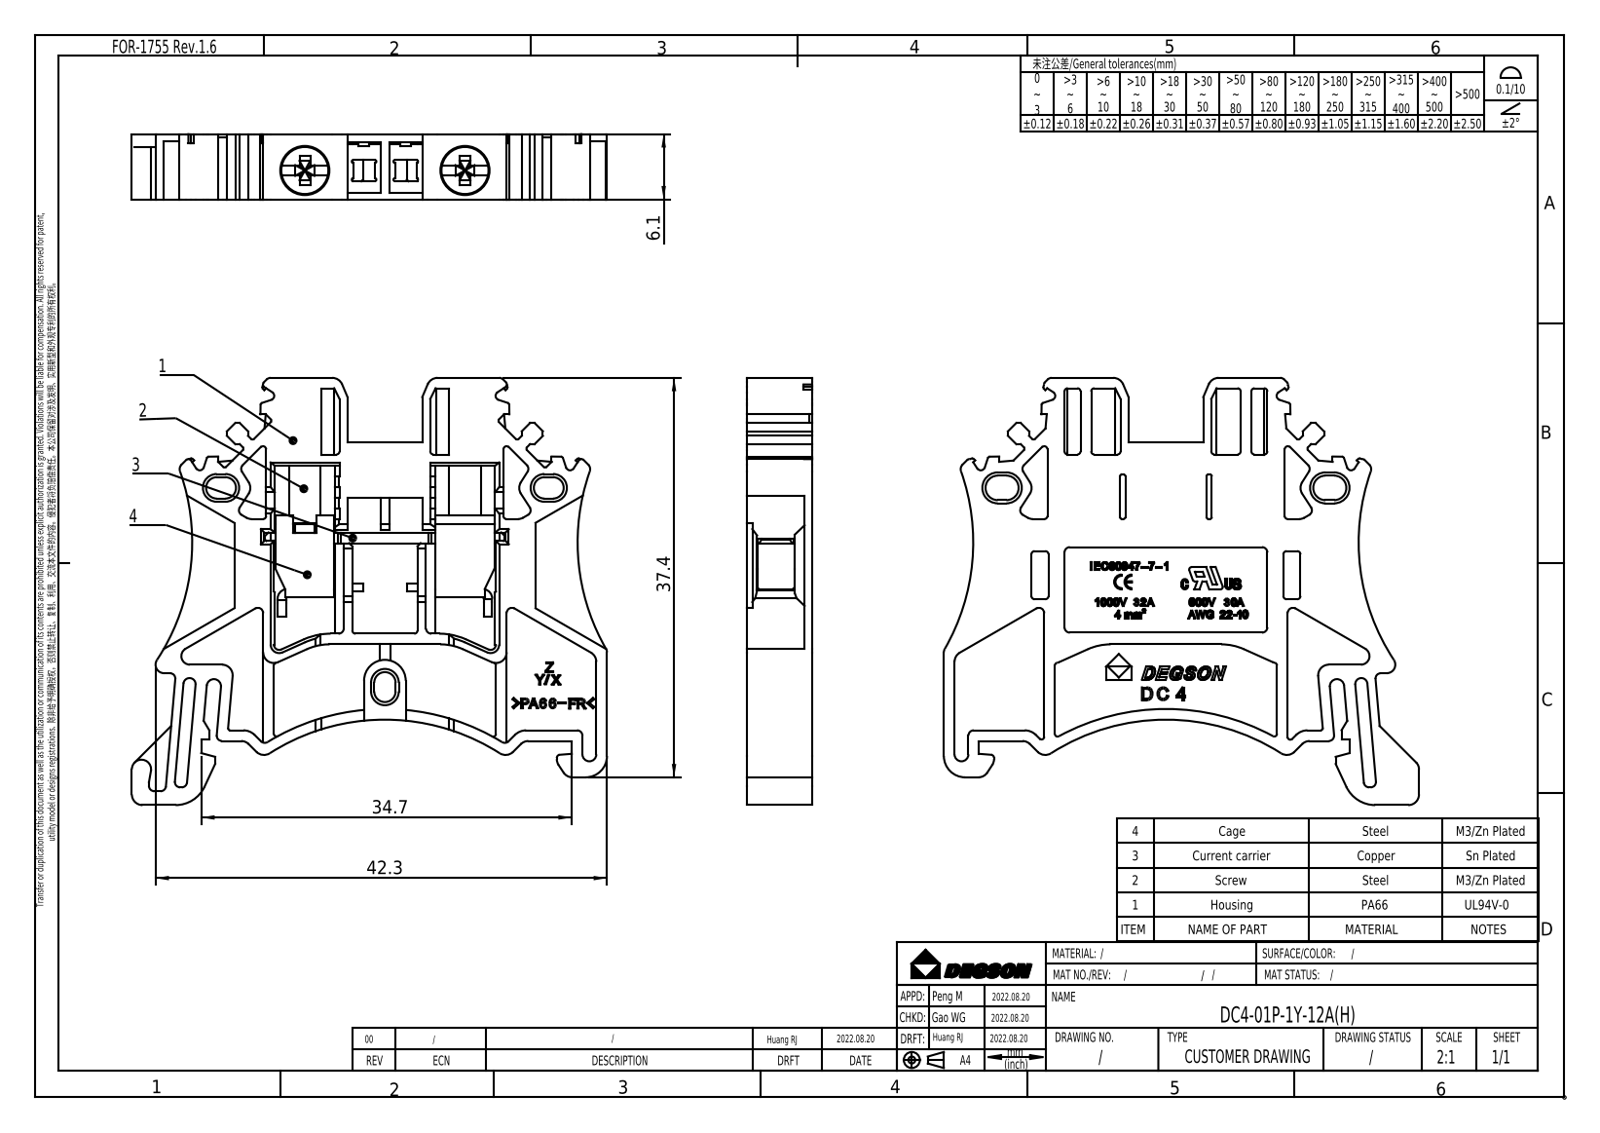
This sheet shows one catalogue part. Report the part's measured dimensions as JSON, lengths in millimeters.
{"part_name": "DC4-01P-1Y-12A(H)-C", "step_written_by": "Solid Edge (AUTOMOTIVE_DESIGN)", "units": "millimeters", "bodies": {"solids": 1, "faces": 2166, "planar": 1945, "cylindrical": 202, "other": 19}, "overall_size": [44.5, 40, 6.1], "volume_mm3": 6000, "surface_area_mm2": 4411, "round_holes": [[4.6, 2]], "partial_cylinders_radius": [[0.3, 32], [0.2, 25], [0.5, 23], [1, 17], [0.25, 6], [0.15, 5], [0.4, 4], [1.15, 4]], "face_to_face_distances": [6.1, 0.75, 5.35, 6, 0.65, 0.7, 0.6, 5.4, 0.8, 1.13], "hole_center_spacings": [15]}
